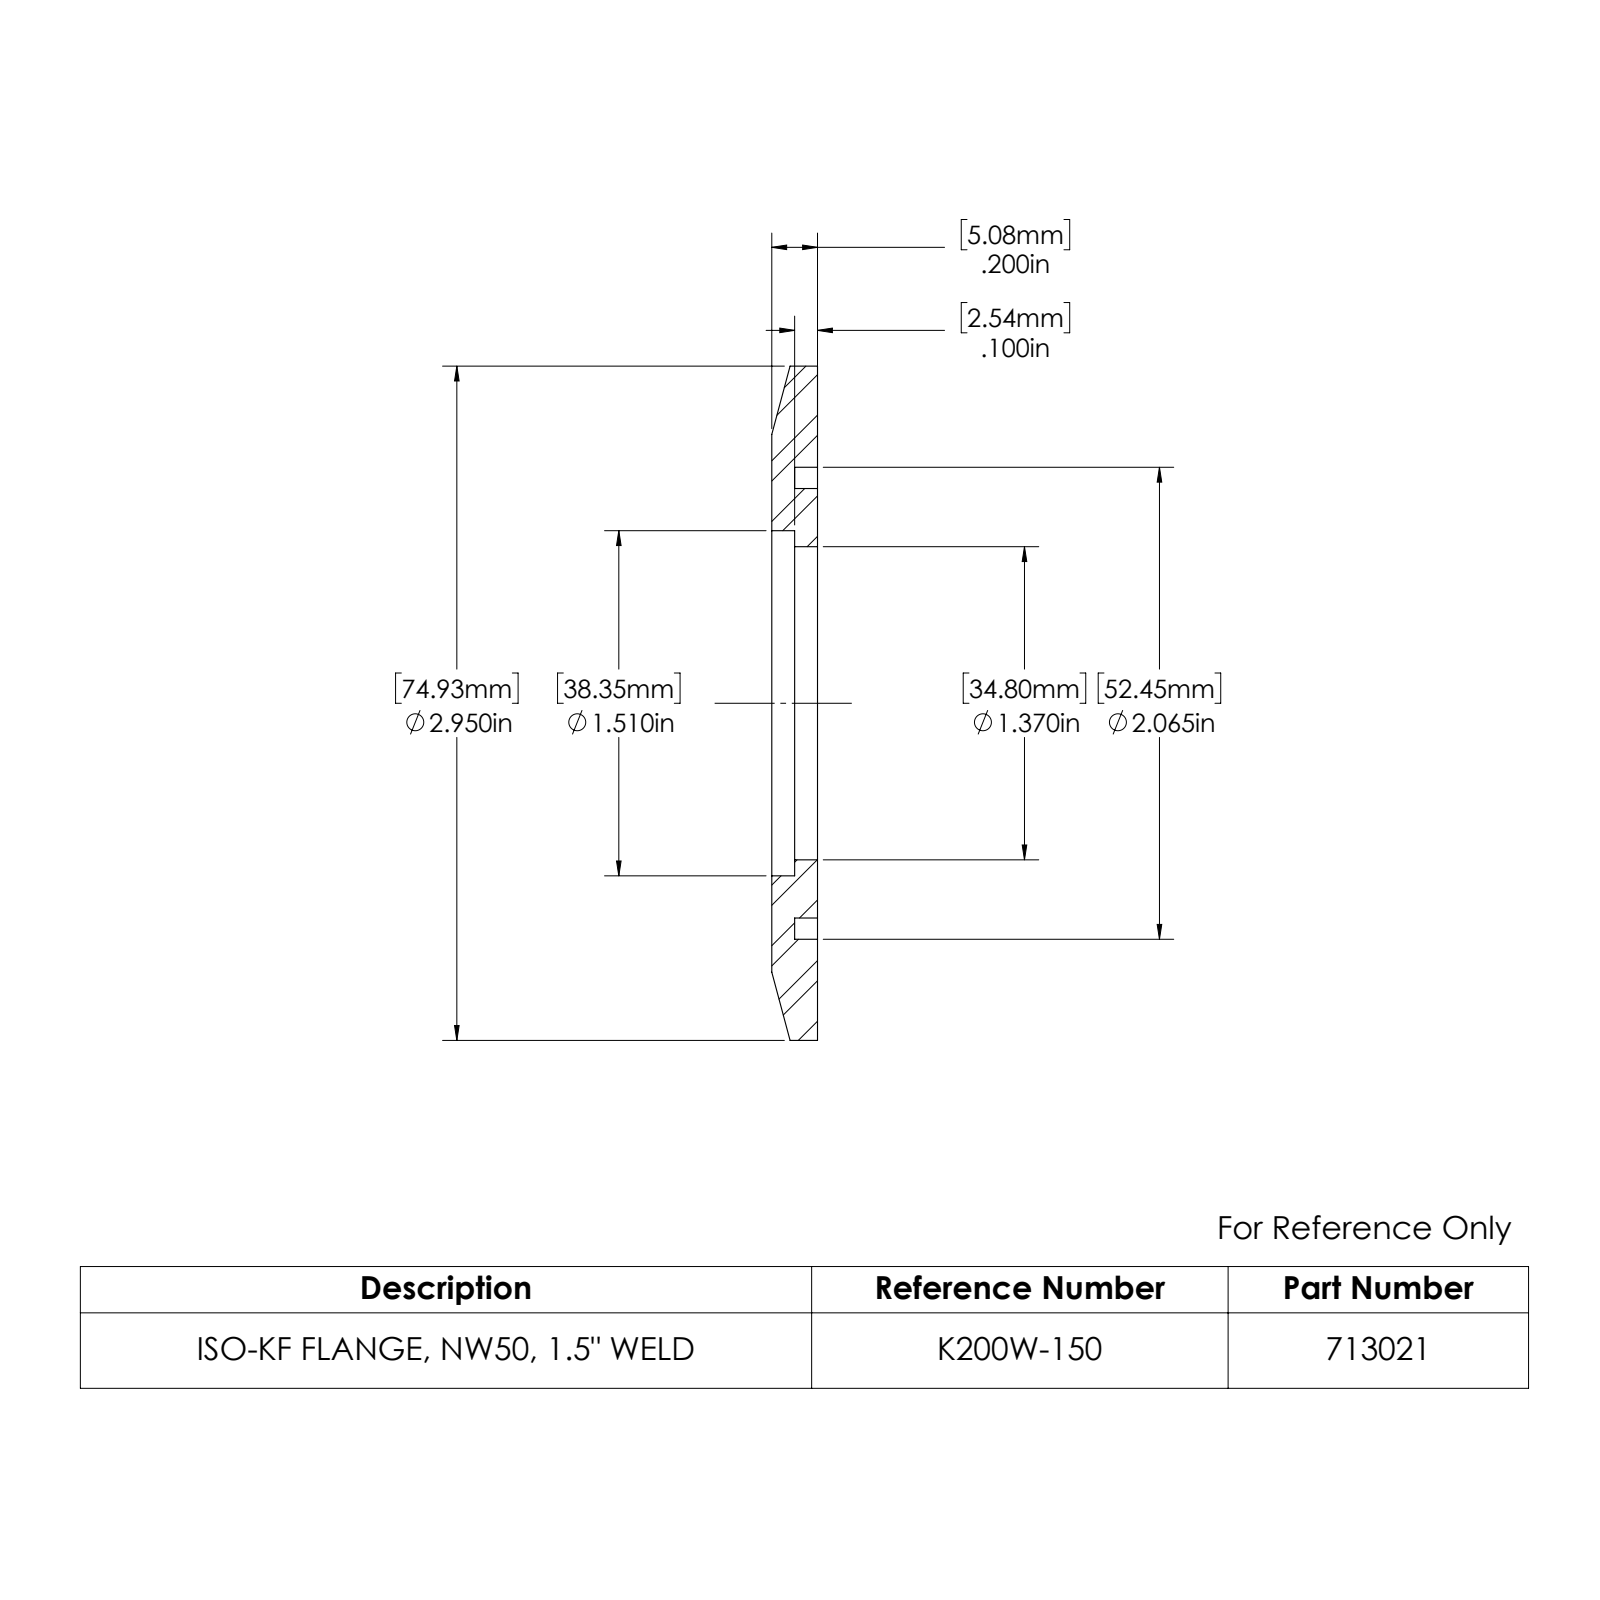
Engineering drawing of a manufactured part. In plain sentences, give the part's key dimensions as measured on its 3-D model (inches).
The part is named "713021". Its 3-D file was written by "SolidWorks 2022 (AUTOMOTIVE_DESIGN)". It is 1 solid with 17 faces: 5 planar, 10 cylindrical and 2 other. Overall it measures 2.95 by 2.95 by 0.2 inches. Its volume is 0.88 cubic inches and its surface area 14.07 square inches. Round holes: 1 of diameter 1.37, 1 of diameter 1.51, 1 of diameter 2.065. Round bosses or shafts: 1 of diameter 2.95, 1 of diameter 1.879. The main face-to-face distances are 0.2, 0.1.
